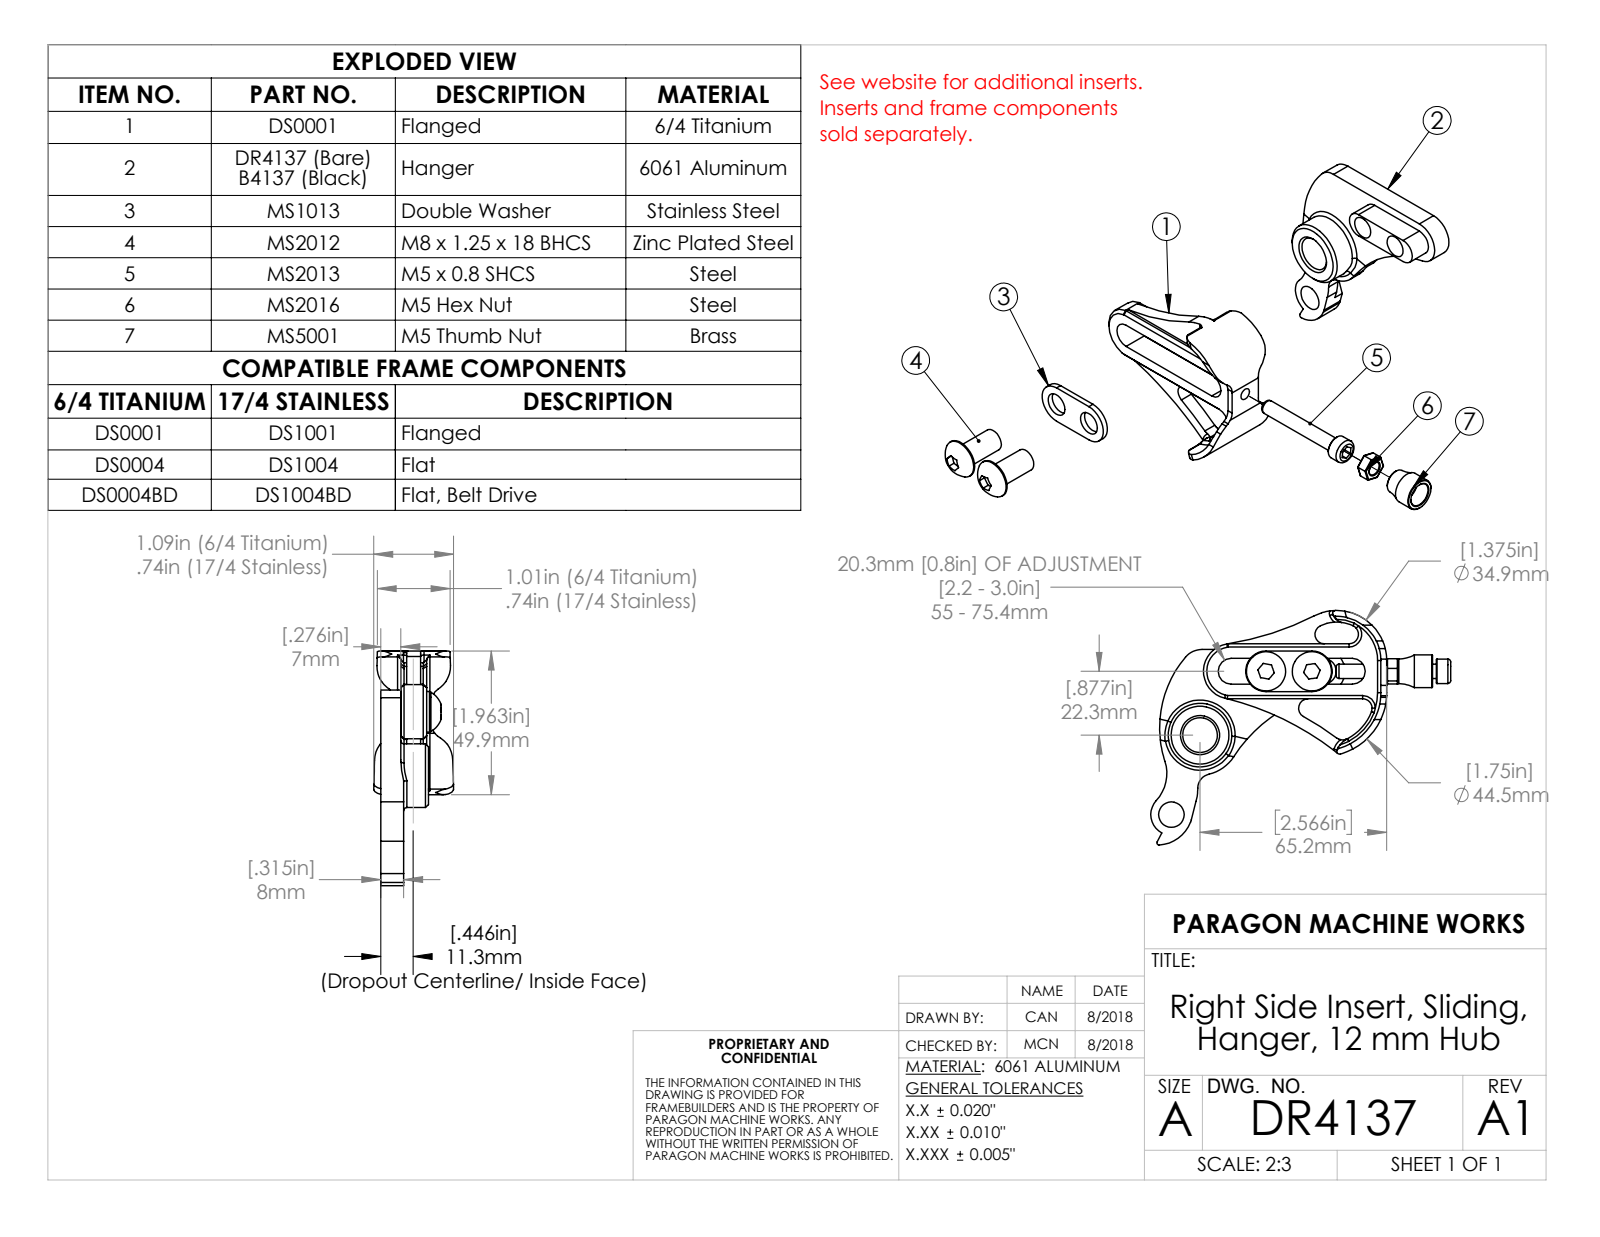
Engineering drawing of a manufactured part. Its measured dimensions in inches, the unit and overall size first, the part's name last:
Units: inches
Overall size (bounding box): 3.131 × 2.358 × 0.656
Round holes (diameter × count): ⌀0.312 ×2, ⌀0.35 ×1, ⌀0.477 ×1
Round bosses / shafts (diameter × count): ⌀0.875 ×1
Partial cylindrical surfaces — rounded edges, fillets, slot ends (radius × count): R0.178 ×2, R0.3 ×2, R0.5 ×2, R0.55 ×2, R0.03 ×1, R0.2 ×1, R0.283 ×1, R0.394 ×1
Main face-to-face distances: 0.276, 0.138, 0.315, 0.177, 0.039, 0.478, 0.356, 0.122, 0.656, 0.518
Hole centre spacings: 0.63, 1.161, 1.262, 1.77, 2.361, 2.759
Volume: 0.968 in³ · Surface area: 12.5 in²
Bodies: 1 solid, 52 faces (13 planar, 30 cylindrical, 9 other)
Part name (STEP PRODUCT): DR4137
STEP written by: SolidWorks 2023 (AUTOMOTIVE_DESIGN)
